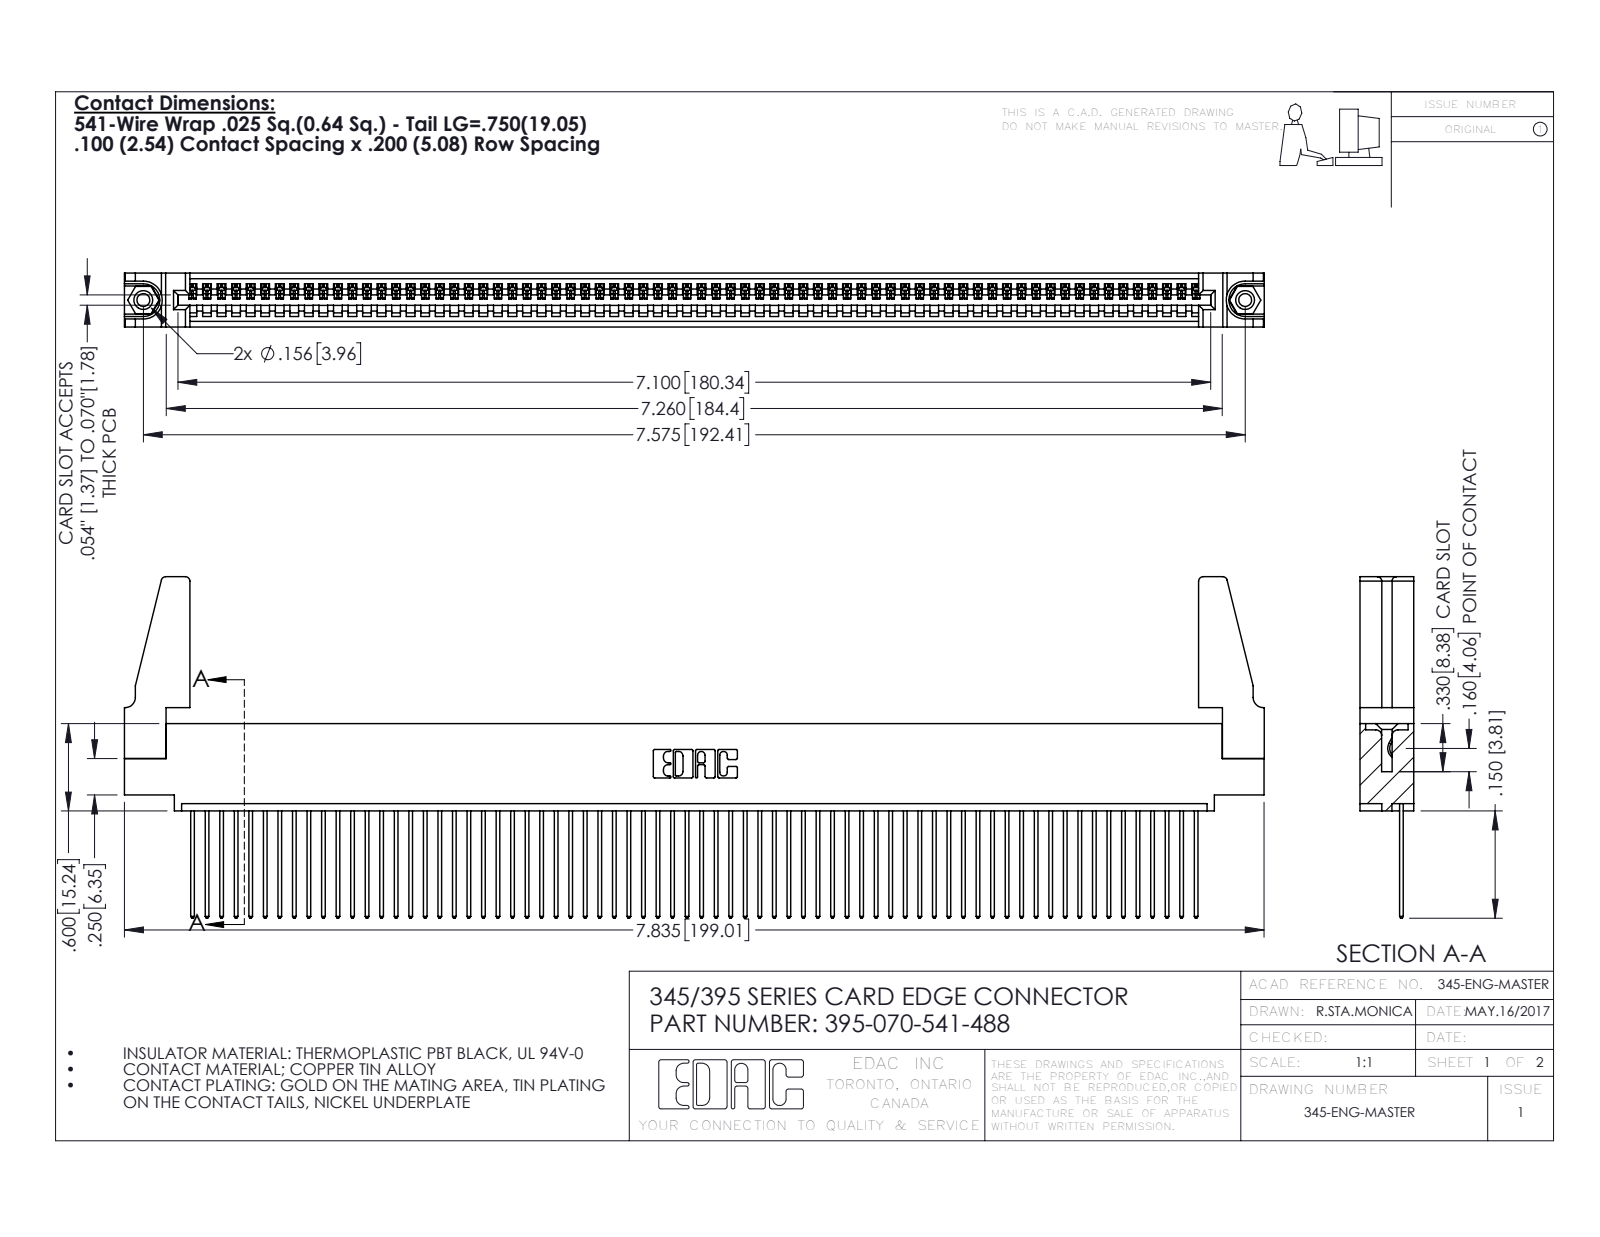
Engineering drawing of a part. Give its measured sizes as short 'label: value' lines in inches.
name: 345-292-001_345-293-141; 345 Part_0.110 Offset - 0.156 Dia-TH; 345-220-078_345-220-088; 395-070-541-488 (+1 more)
written by: SolidWorks 2016 (CONFIG_CONTROL_DESIGN)
unit: in
bodies: 75 solids, 4314 faces (2956 planar, 1342 cylindrical, 16 other)
size: 7.836 × 2.347 × 0.37
volume: 1.376 in³; area: 47.41 in²
holes: 2× ⌀0.089, 2× ⌀0.125, 2× ⌀0.156, 1× ⌀0.064
bosses: 2× ⌀0.155
rounds: 140× R0.006, 140× R0.01, 22× R0.01, 8× R0.03, 6× R0.007, 6× R0.031, 3× R0.026, 2× R0.031
face distances: 0.072, 0.298, 0.37, 0.098, 0.272, 0.025, 0.2, 0.225, 0.149, 0.072
hole spacings: 0.27, 7.339, 7.575
